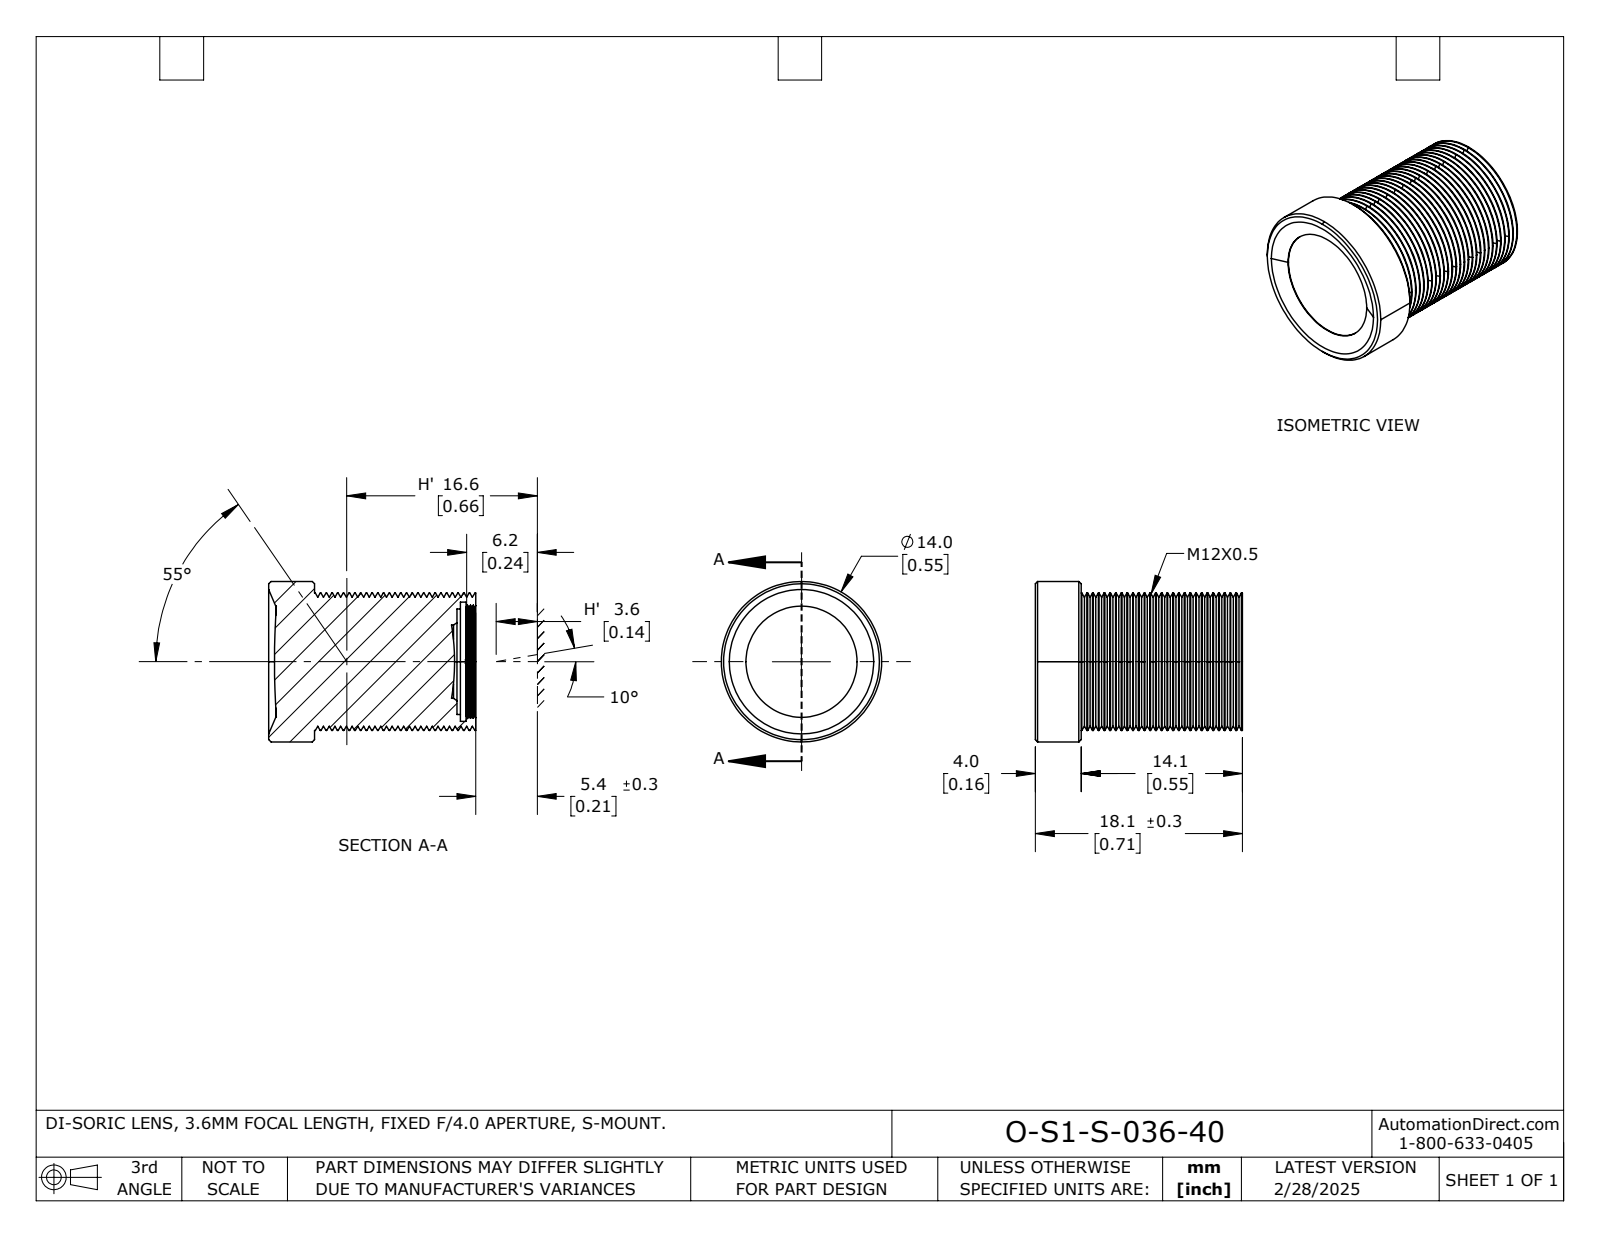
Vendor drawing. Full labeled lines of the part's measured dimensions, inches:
Part name (STEP PRODUCT): O-S1-S-036-40--213094
STEP written by: SolidWorks 2024 (AUTOMOTIVE_DESIGN)
Units: inches
Bodies: 1 solid, 220 faces (6 planar, 76 cylindrical, 138 other)
Overall size (bounding box): 0.712 × 0.551 × 0.551
Volume: 0.118 in³ · Surface area: 2.398 in²
Round holes (diameter × count): ⌀0.252 ×1, ⌀0.362 ×1, ⌀0.374 ×1, ⌀0.382 ×1, ⌀0.409 ×1
Round bosses / shafts (diameter × count): ⌀0.551 ×1, ⌀0.472 ×1
Main face-to-face distances: 0.555, 0.49, 0.065, 0.157, 0.647, 0.712, 0.659, 0.502, 0.053, 0.679
